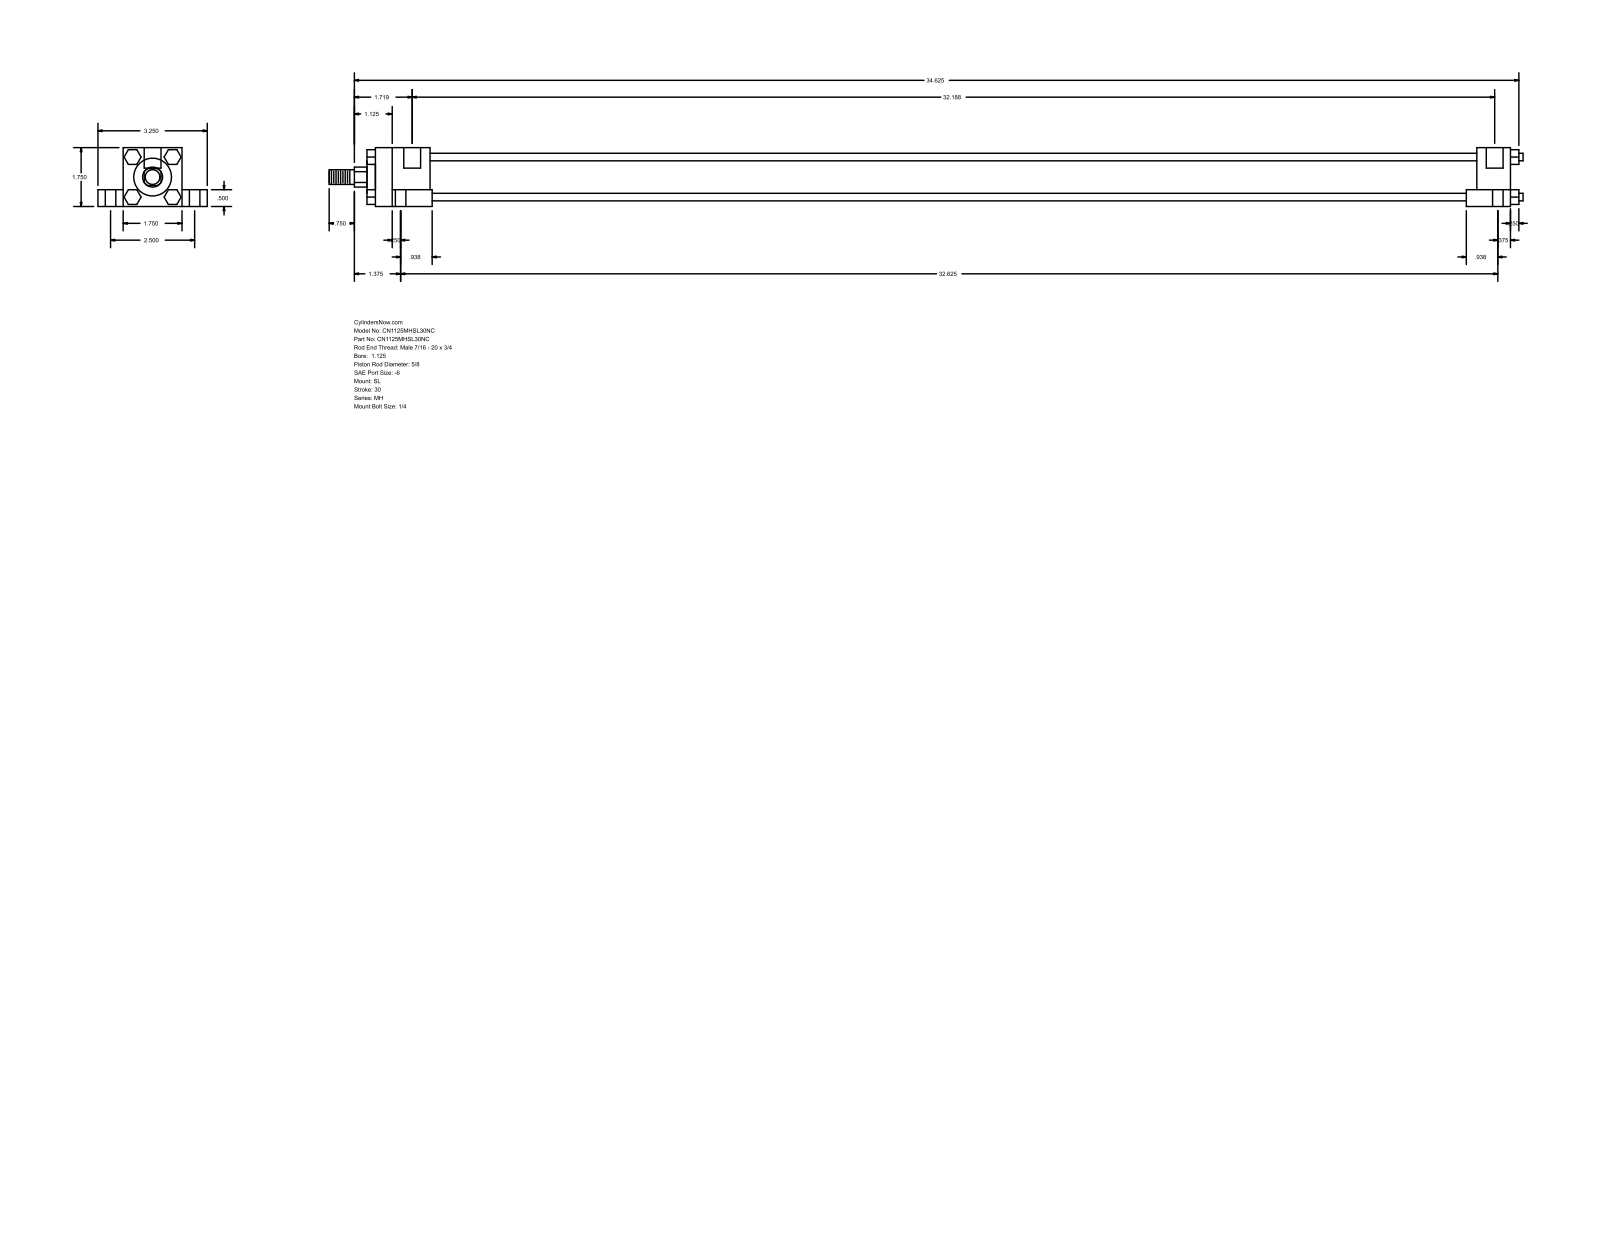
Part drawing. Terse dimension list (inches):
name: MH_SL__0112_0.625
written by: GSSL Pune (CONFIG_CONTROL_DESIGN)
unit: in
bodies: 0 solids, 150 faces (114 planar, 36 cylindrical, 0 other)
size: 35.5 × 3.25 × 1.75
holes: 4× ⌀0.219, 4× ⌀0.313, 4× ⌀0.563, 2× ⌀0.5
bosses: 4× ⌀0.225, 1× ⌀1.375, 1× ⌀1.125, 1× ⌀0.625, 1× ⌀0.437
rounds: 1× R0.297
face distances: 1.75, 0.75, 0.5, 1.25, 2.5, 0.437, 1.875, 31.125, 32.125, 1
hole spacings: 1.254, 1.269, 1.296, 2.5, 32.063, 32.181, 32.305, 32.43
